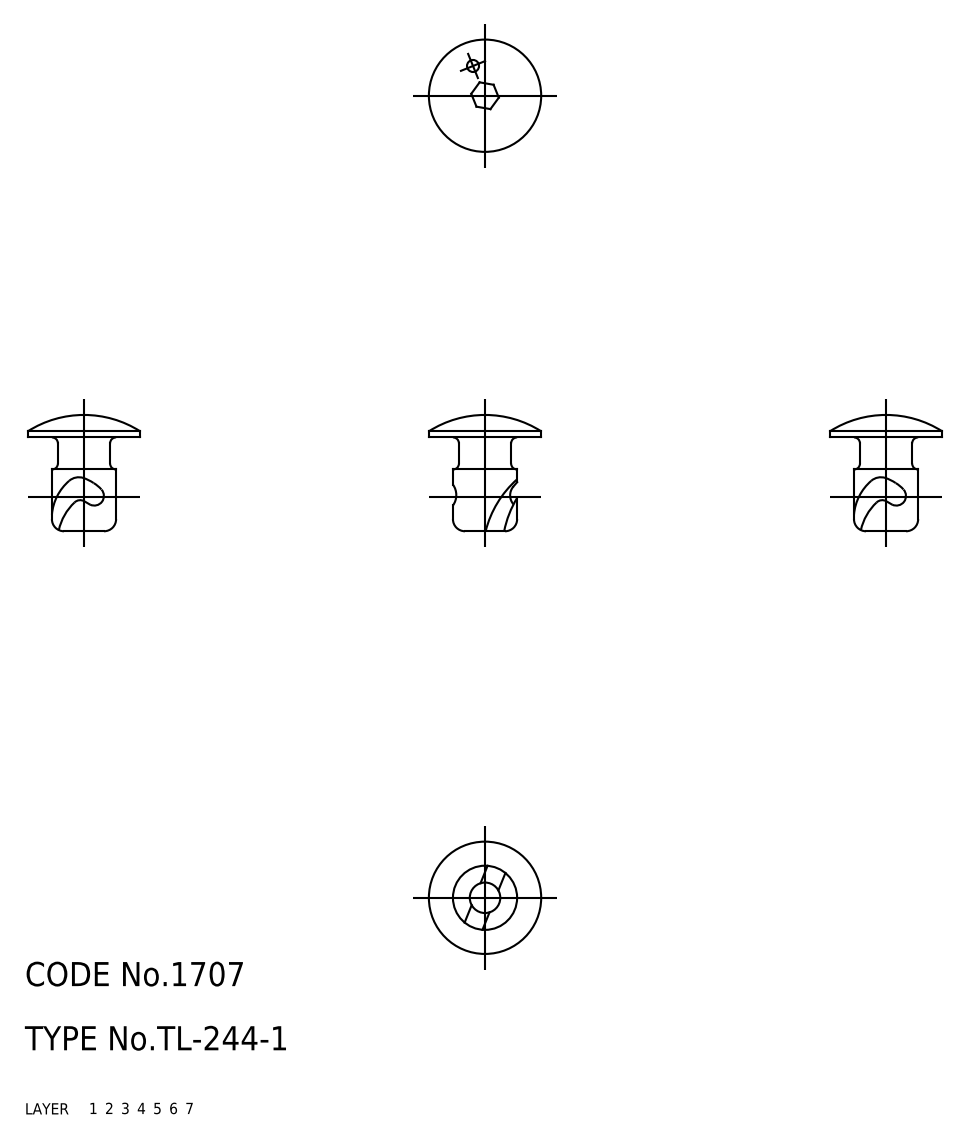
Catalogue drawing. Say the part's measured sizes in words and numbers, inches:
The part is named "67112813". Its 3-D file was written by "CADfix (AUTOMOTIVE_DESIGN)". It is 1 solid with 36 faces: 0 planar, 0 cylindrical and 36 other. Overall it measures 0.567 by 0.551 by 0.551 inches. Its volume is 0.037 cubic inches and its surface area 1.15 square inches.
